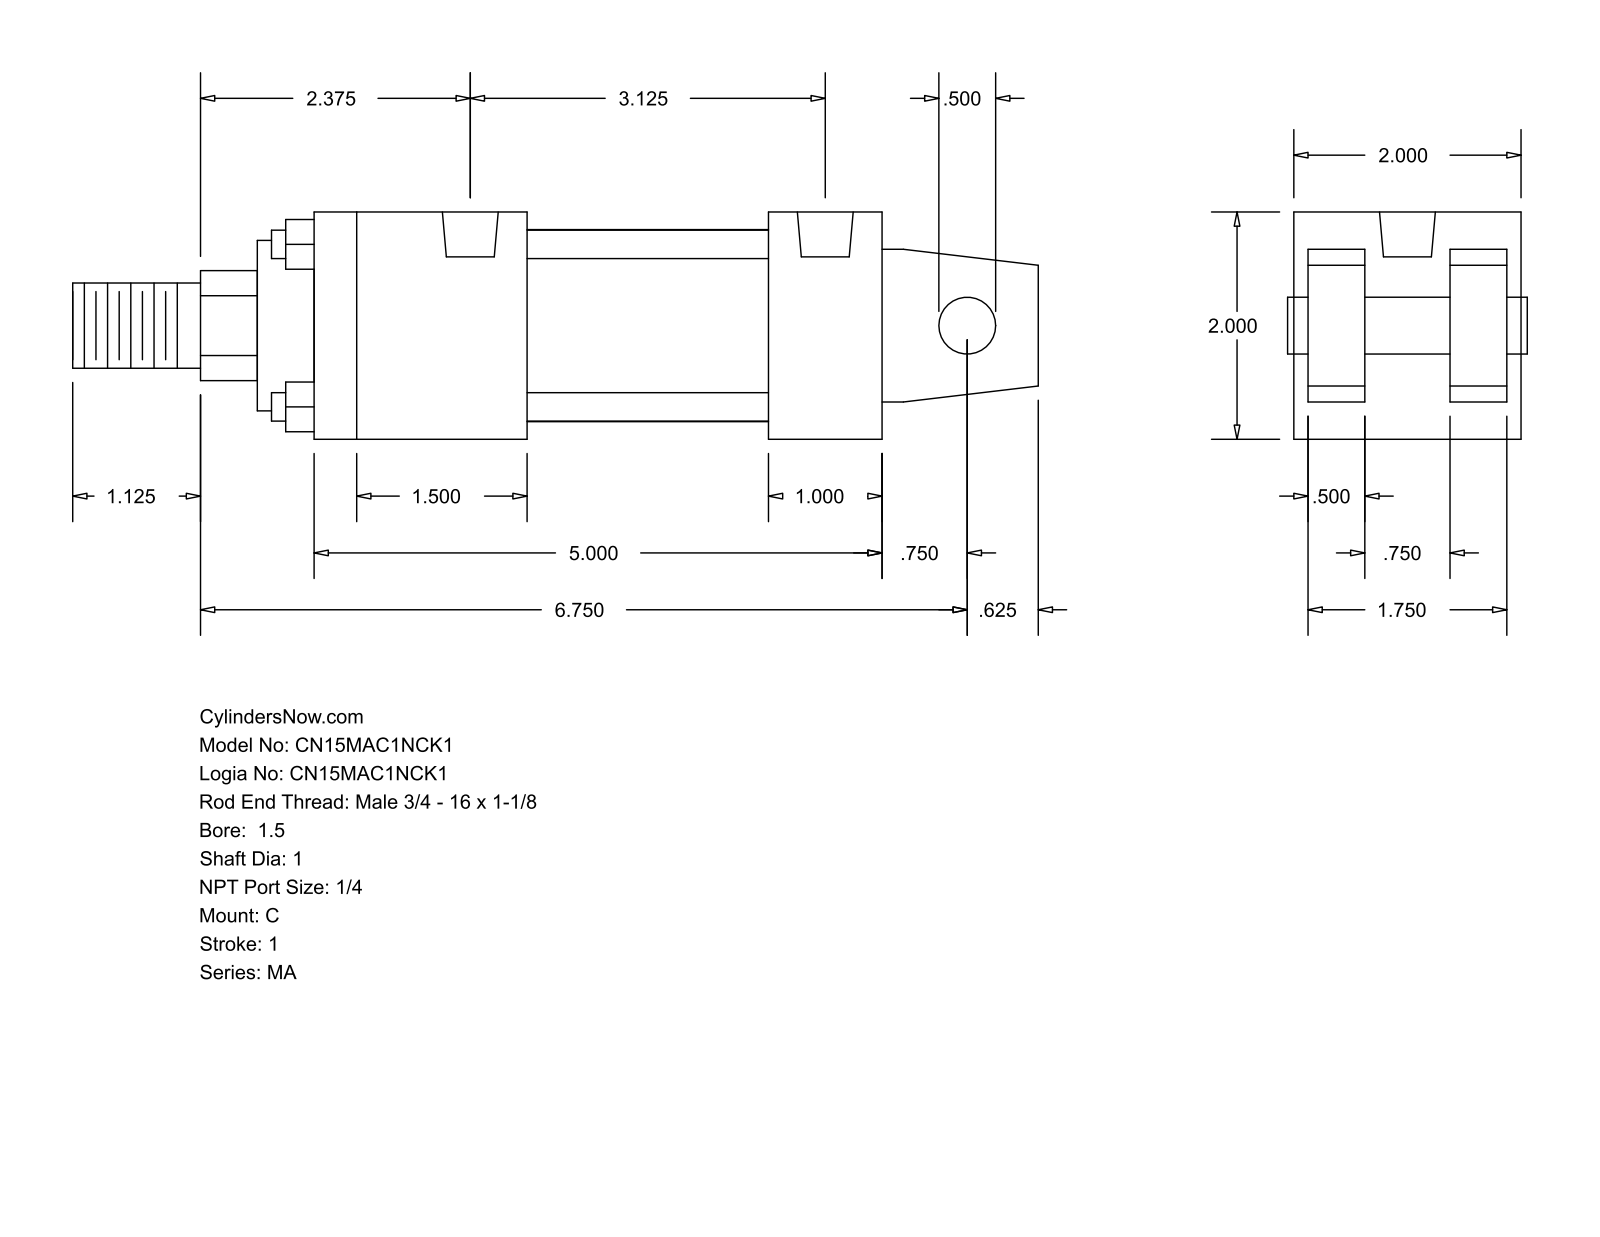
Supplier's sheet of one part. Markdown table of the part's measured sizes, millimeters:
| quantity | value |
| --- | --- |
| part name | MA_C__0150_1 |
| STEP written by | GSSL Pune (CONFIG_CONTROL_DESIGN) |
| units | millimeters |
| bodies | 0 solids, 103 faces (76 planar, 27 cylindrical, 0 other) |
| overall size | 215.9 × 50.8 × 50.8 |
| round holes (diameter × count) | 7.94 × 4, 12.49 × 2 |
| round bosses / shafts (diameter × count) | 6.35 × 4, 42.93 × 1, 38.1 × 1, 25.4 × 1, 19.05 × 1, 12.7 × 1 |
| partial cylindrical surfaces (radius × count) | 12.29 × 1 |
| main face-to-face distances | 50.8, 47.63, 12.7, 3.17, 15.87, 34.93, 31.76, 101.6, 53.97, 127 |
| hole center spacings | 79.37 |
